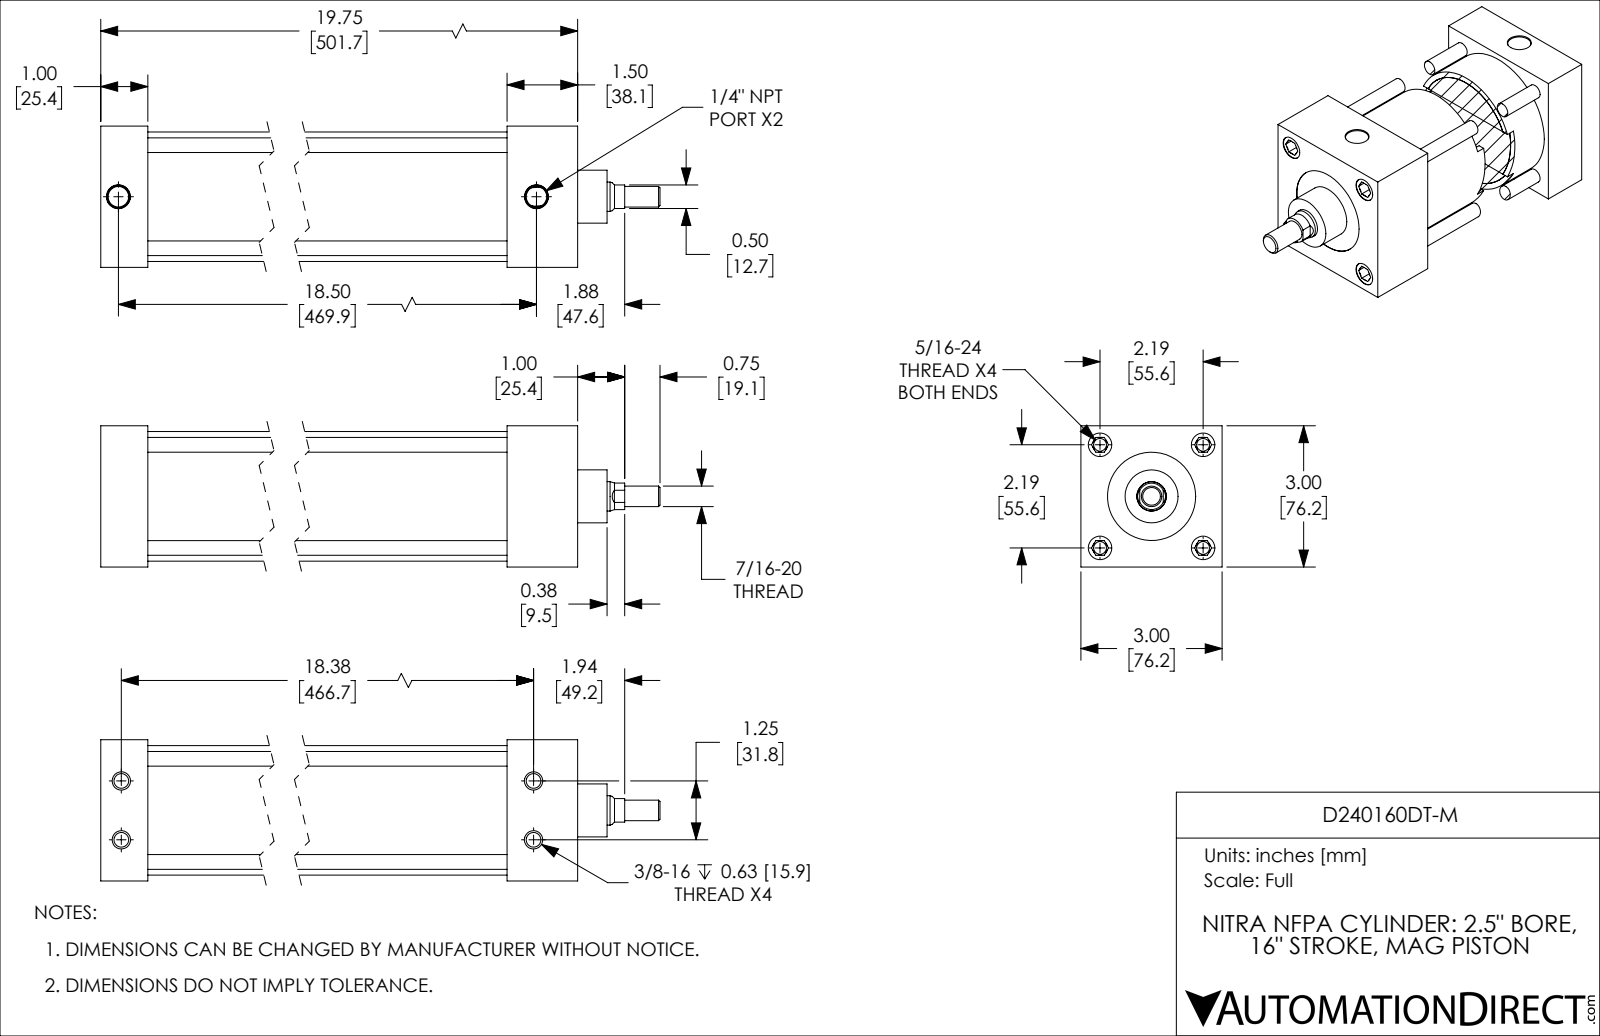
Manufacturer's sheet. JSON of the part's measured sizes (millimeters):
{"part_name": "D240160DT-M_BODY; D240160DT-M_PISTON_KK1; D240160DT-M", "step_written_by": "SolidWorks 2019 (CONFIG_CONTROL_DESIGN)", "units": "millimeters", "bodies": {"solids": 2, "faces": 200, "planar": 58, "cylindrical": 62, "other": 80}, "overall_size": [546.1, 76.2, 76.2], "volume_mm3": 922900, "surface_area_mm2": 316300, "round_holes": [[6.9, 4], [8, 4], [12.7, 4], [11.1, 2], [15.9, 1], [47.6, 1], [63.5, 1]], "round_bosses_or_shafts": [[7.9, 4], [69.9, 1], [63.5, 1], [28.6, 1], [15.8, 1], [11.1, 1]], "partial_cylinders_radius": [[7.1, 1]], "face_to_face_distances": [76.2, 25.4, 463.6, 438.2, 501.7, 476.3, 38.1, 31.8, 57.2, 406.4], "hole_center_spacings": [39.3, 55.6, 468.6, 16, 16, 31.8, 78.7, 466.7]}
